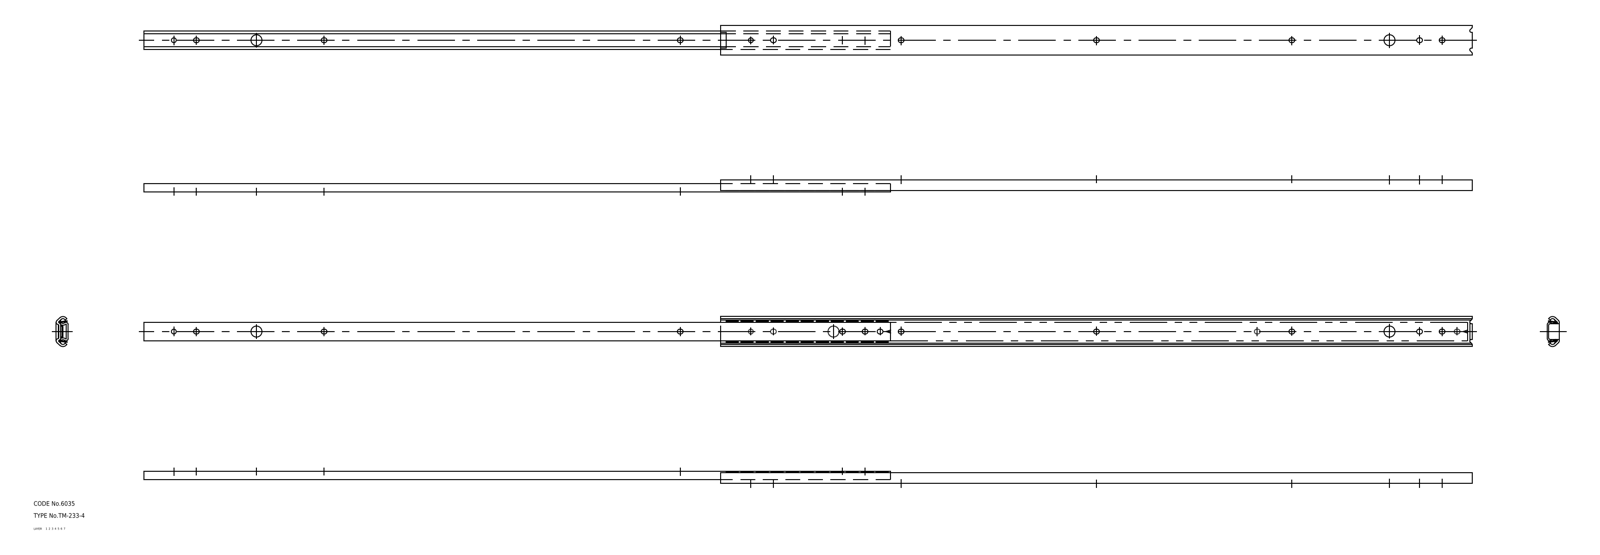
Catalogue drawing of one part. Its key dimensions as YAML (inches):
part_name: "ball; retainer; member_B; member_A (+1 more)"
step_written_by: "CADfix (AUTOMOTIVE_DESIGN)"
units: inches
bodies: {solids: 25, faces: 378, planar: 0, cylindrical: 0, other: 378}
overall_size: [34.803, 0.787, 0.315]
volume: 1.959
surface_area: 86.01
